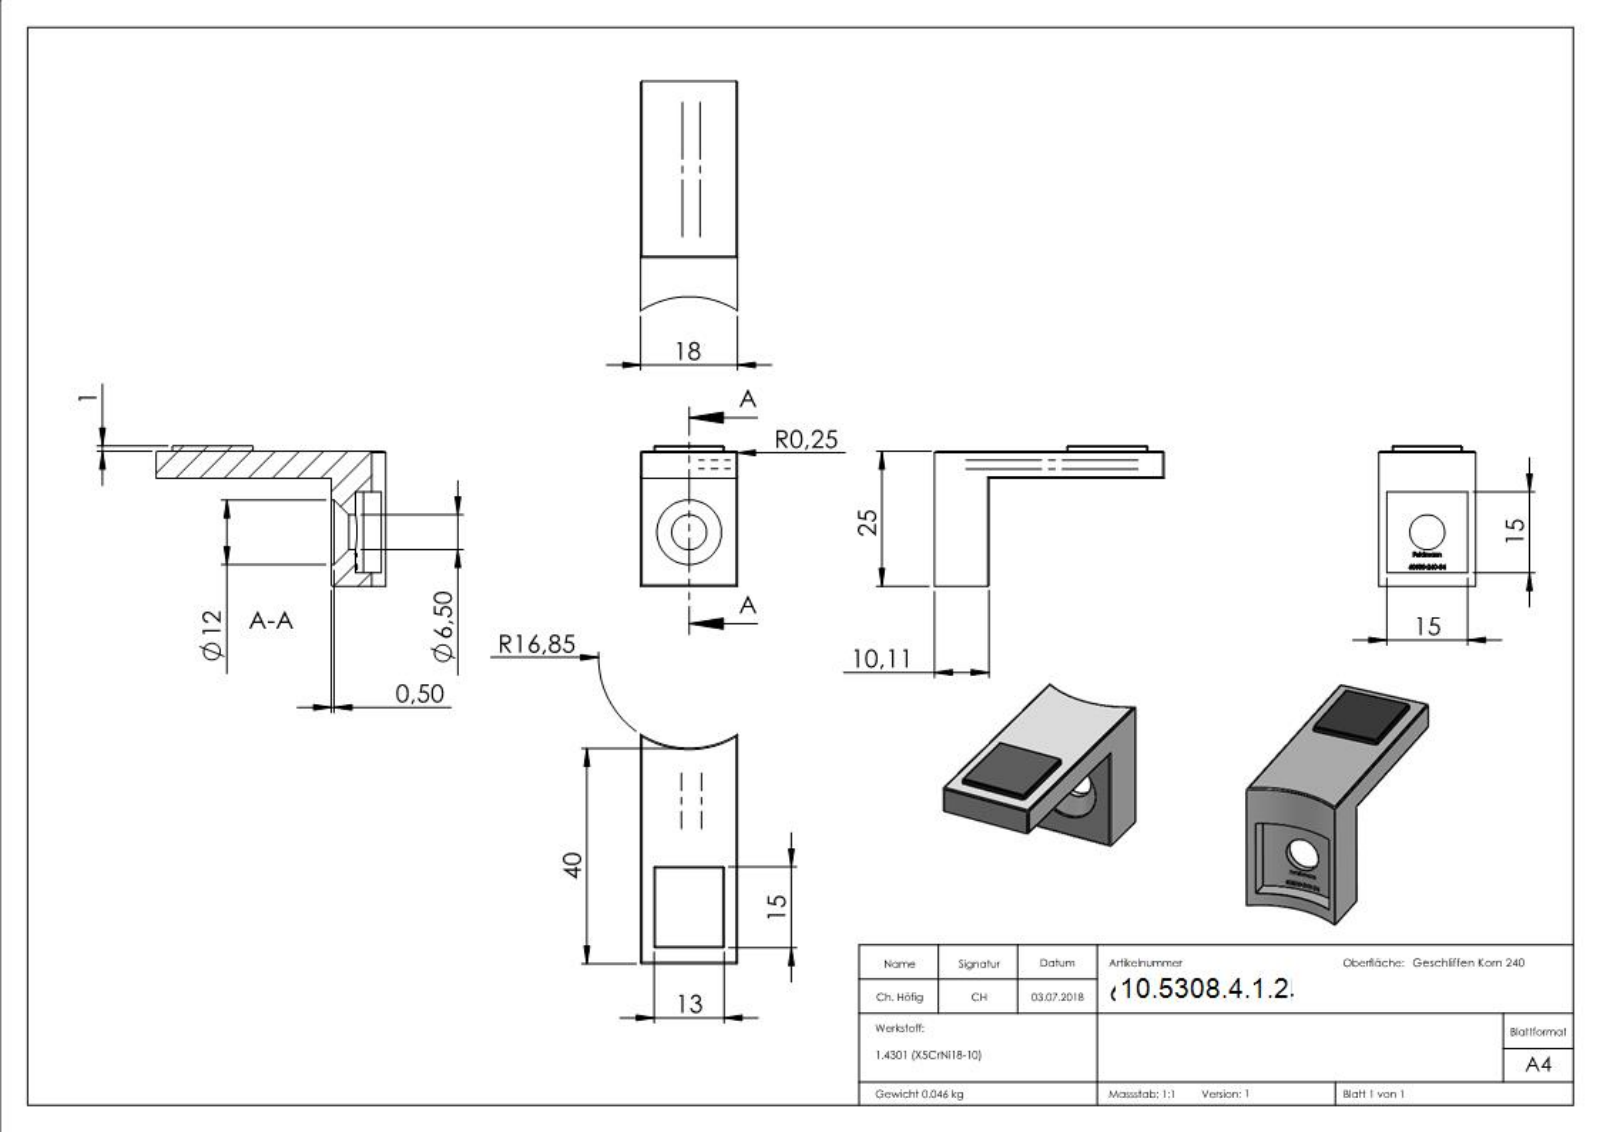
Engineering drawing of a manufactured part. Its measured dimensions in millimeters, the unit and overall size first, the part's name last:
Units: millimetres
Overall size (bounding box): 42.6 × 26 × 18
Round holes (diameter × count): ⌀6.5 ×1, ⌀12 ×1
Partial cylindrical surfaces — rounded edges, fillets, slot ends (radius × count): R0.25 ×10, R0.2 ×8, R16.85 ×1, R19.85 ×1, R19.95 ×1
Main face-to-face distances: 5, 18, 1, 6, 20, 25, 26, 2.5, 15, 1.5
Volume: 5 883 mm³ · Surface area: 3 848 mm²
Bodies: 2 solids, 308 faces (123 planar, 57 cylindrical, 128 other)
Part name (STEP PRODUCT): 60500-240-34
STEP written by: SolidWorks 2015 (CONFIG_CONTROL_DESIGN)
